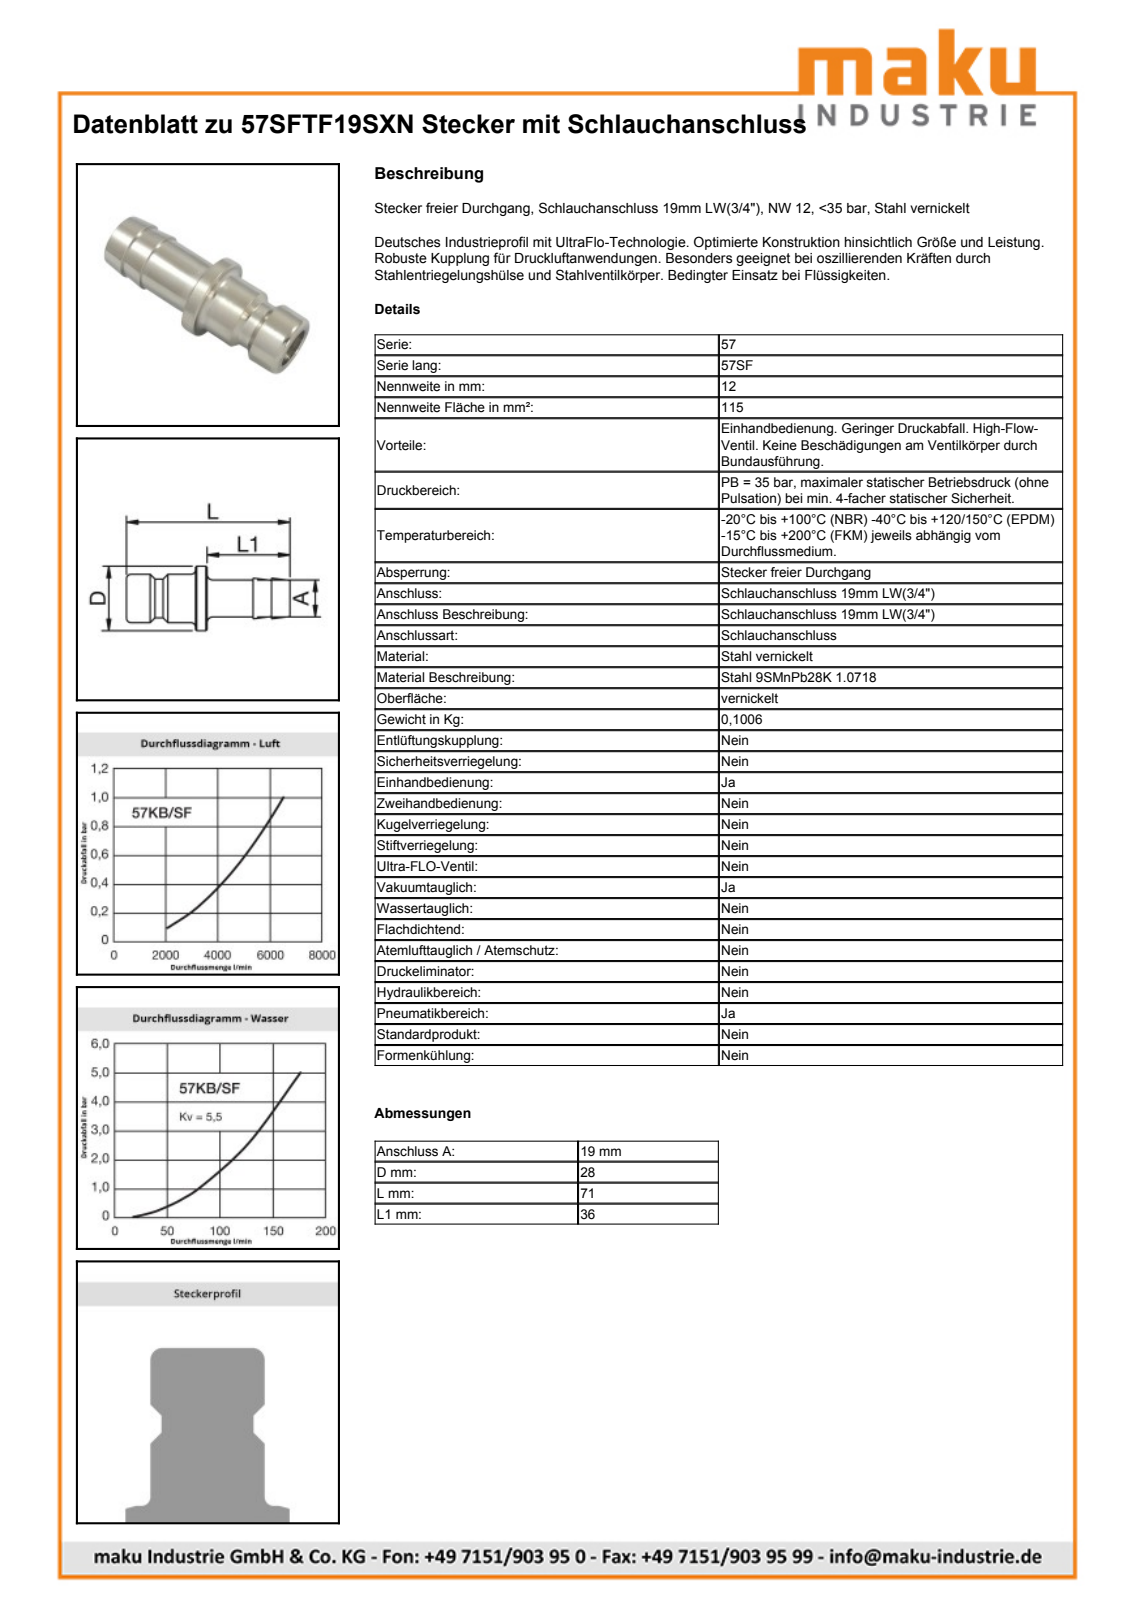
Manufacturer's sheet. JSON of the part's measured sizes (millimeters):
{"part_name": "D110177", "step_written_by": "Autodesk Inventor 2013 (AUTOMOTIVE_DESIGN)", "units": "millimeters", "bodies": {"solids": 1, "faces": 24, "planar": 6, "cylindrical": 6, "other": 12}, "overall_size": [63, 28, 28], "volume_mm3": 12011, "surface_area_mm2": 7621, "round_holes": [[13.5, 1]], "round_bosses_or_shafts": [[28, 1], [20.9, 1], [19, 1], [16.8, 1]], "face_to_face_distances": [28, 5, 33, 30, 35, 63, 6, 51, 21, 16]}
